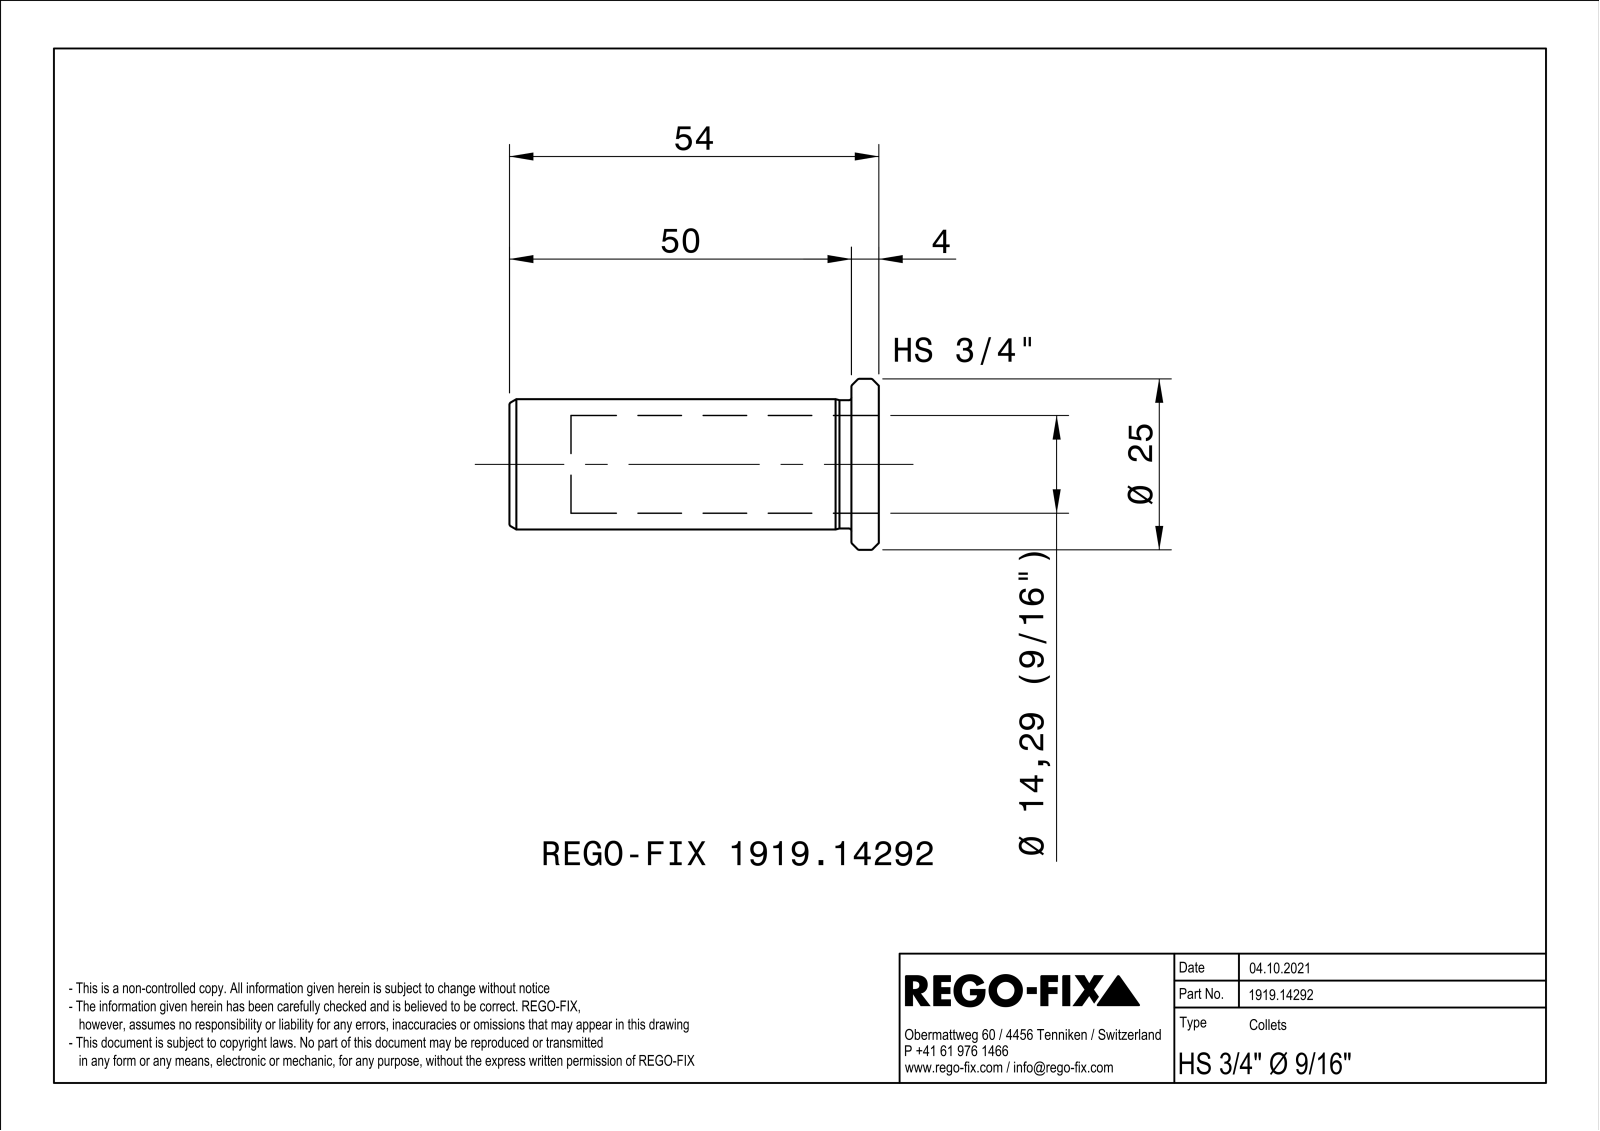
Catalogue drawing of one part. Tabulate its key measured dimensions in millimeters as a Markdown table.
| quantity | value |
| --- | --- |
| part name | NOCUT |
| STEP written by | SIEMENS PLM Software Solid Edge ST10 (AUTOMOTIVE_DESIGN) |
| units | millimeters |
| bodies | 1 solid, 70 faces (22 planar, 11 cylindrical, 37 other) |
| overall size | 54 × 24.98 × 24.98 |
| volume | 6 608 mm³ |
| surface area | 6 796 mm² |
| round holes (diameter × count) | 14.29 × 1, 16.5 × 1 |
| round bosses / shafts (diameter × count) | 25 × 1, 19.05 × 1, 18.75 × 1 |
| main face-to-face distances | 1, 4, 54, 50 |
